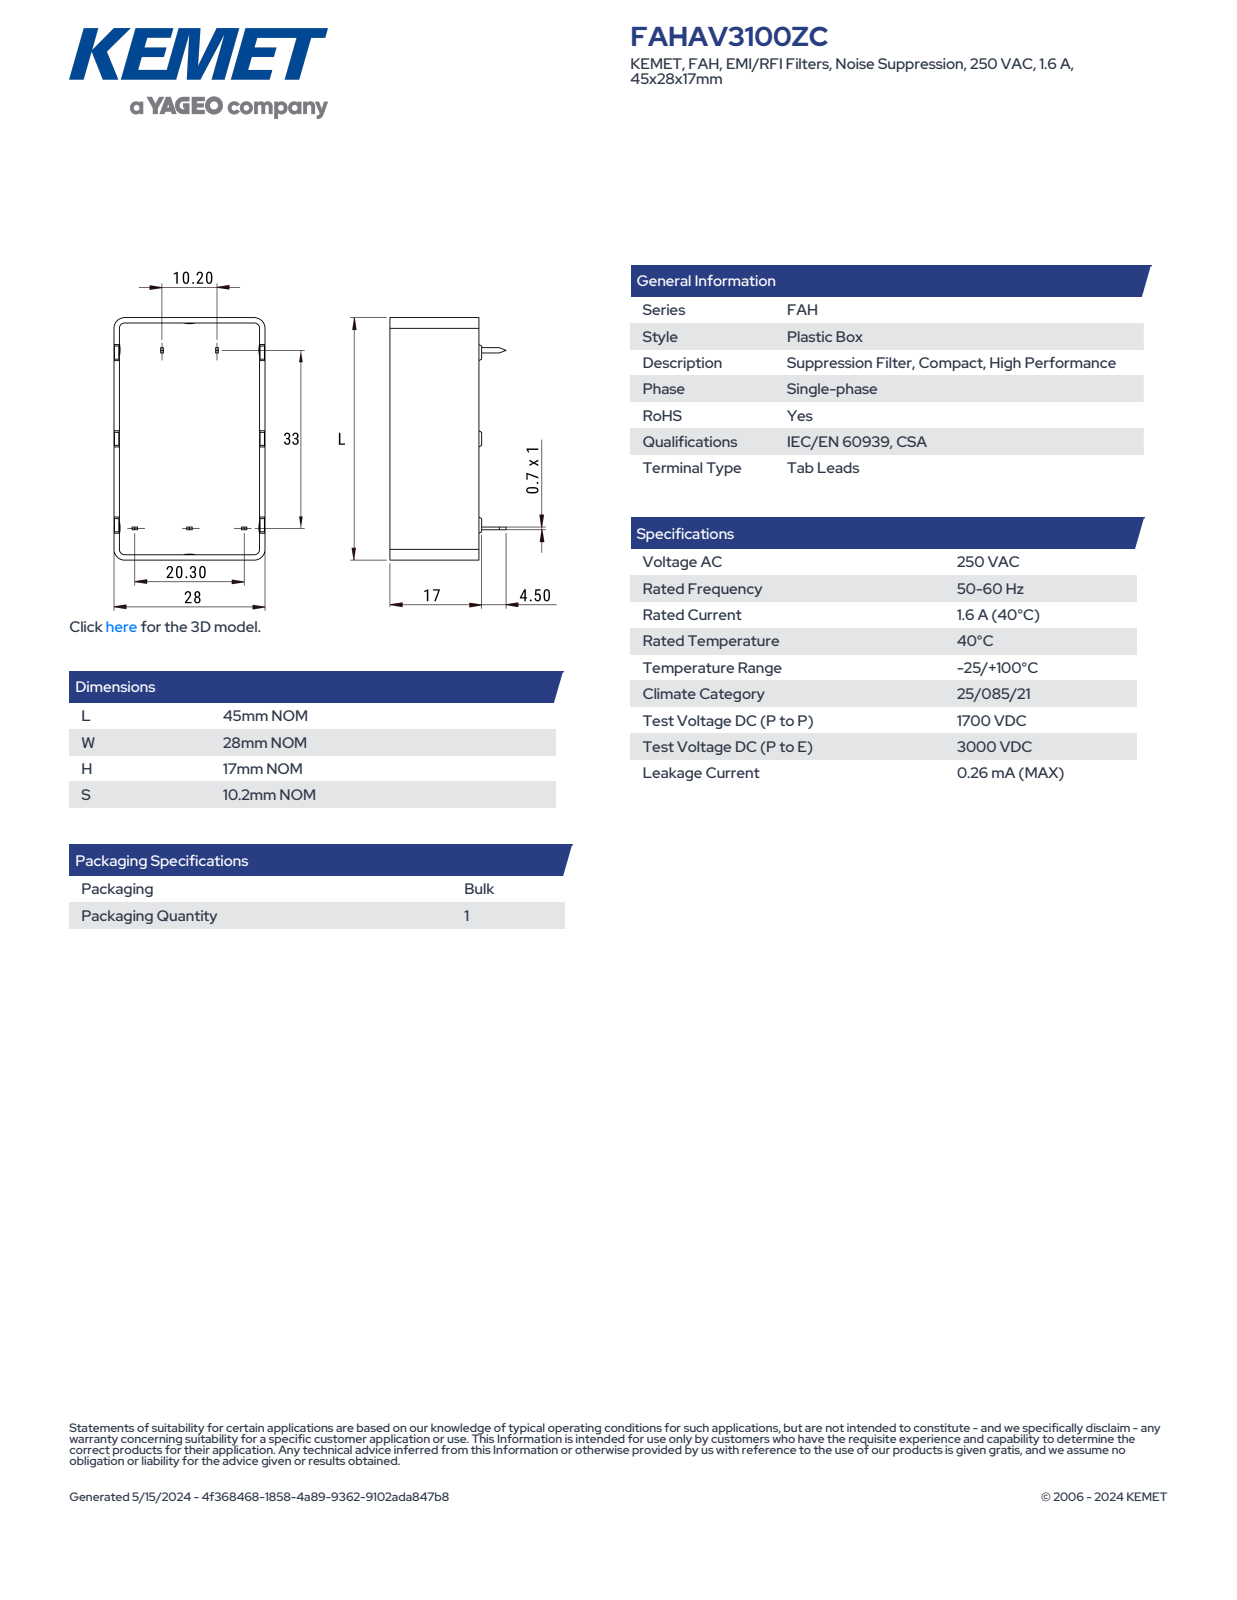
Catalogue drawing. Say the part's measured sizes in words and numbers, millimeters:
The part is named "20300484500; EFC_KFAHAV_L45W28H17; 20051002600; 20042000500 (+1 more)". Its 3-D file was written by "SolidWorks 2014 (AUTOMOTIVE_DESIGN)". It is 8 solids with 474 faces: 271 planar, 109 cylindrical and 94 other. Overall it measures 45 by 28 by 21.5 millimeters. Its volume is 20 200 cubic millimeters and its surface area 15 921 square millimeters. Round holes: 5 of diameter 2.1, 5 of diameter 3.4, 5 of diameter 5.2. Partial cylindrical surfaces (rounded edges, fillets, slot ends): 14 of radius 1, 4 of radius 2, 3 of radius 0.8, 3 of radius 1.3. The main face-to-face distances are 1, 12.1, 13.1, 27, 14, 0.9, 13, 2, 26, 3. The hole center spacings are 10.15, 29.3, 30.58, 34.9, 17.7, 20.3.
